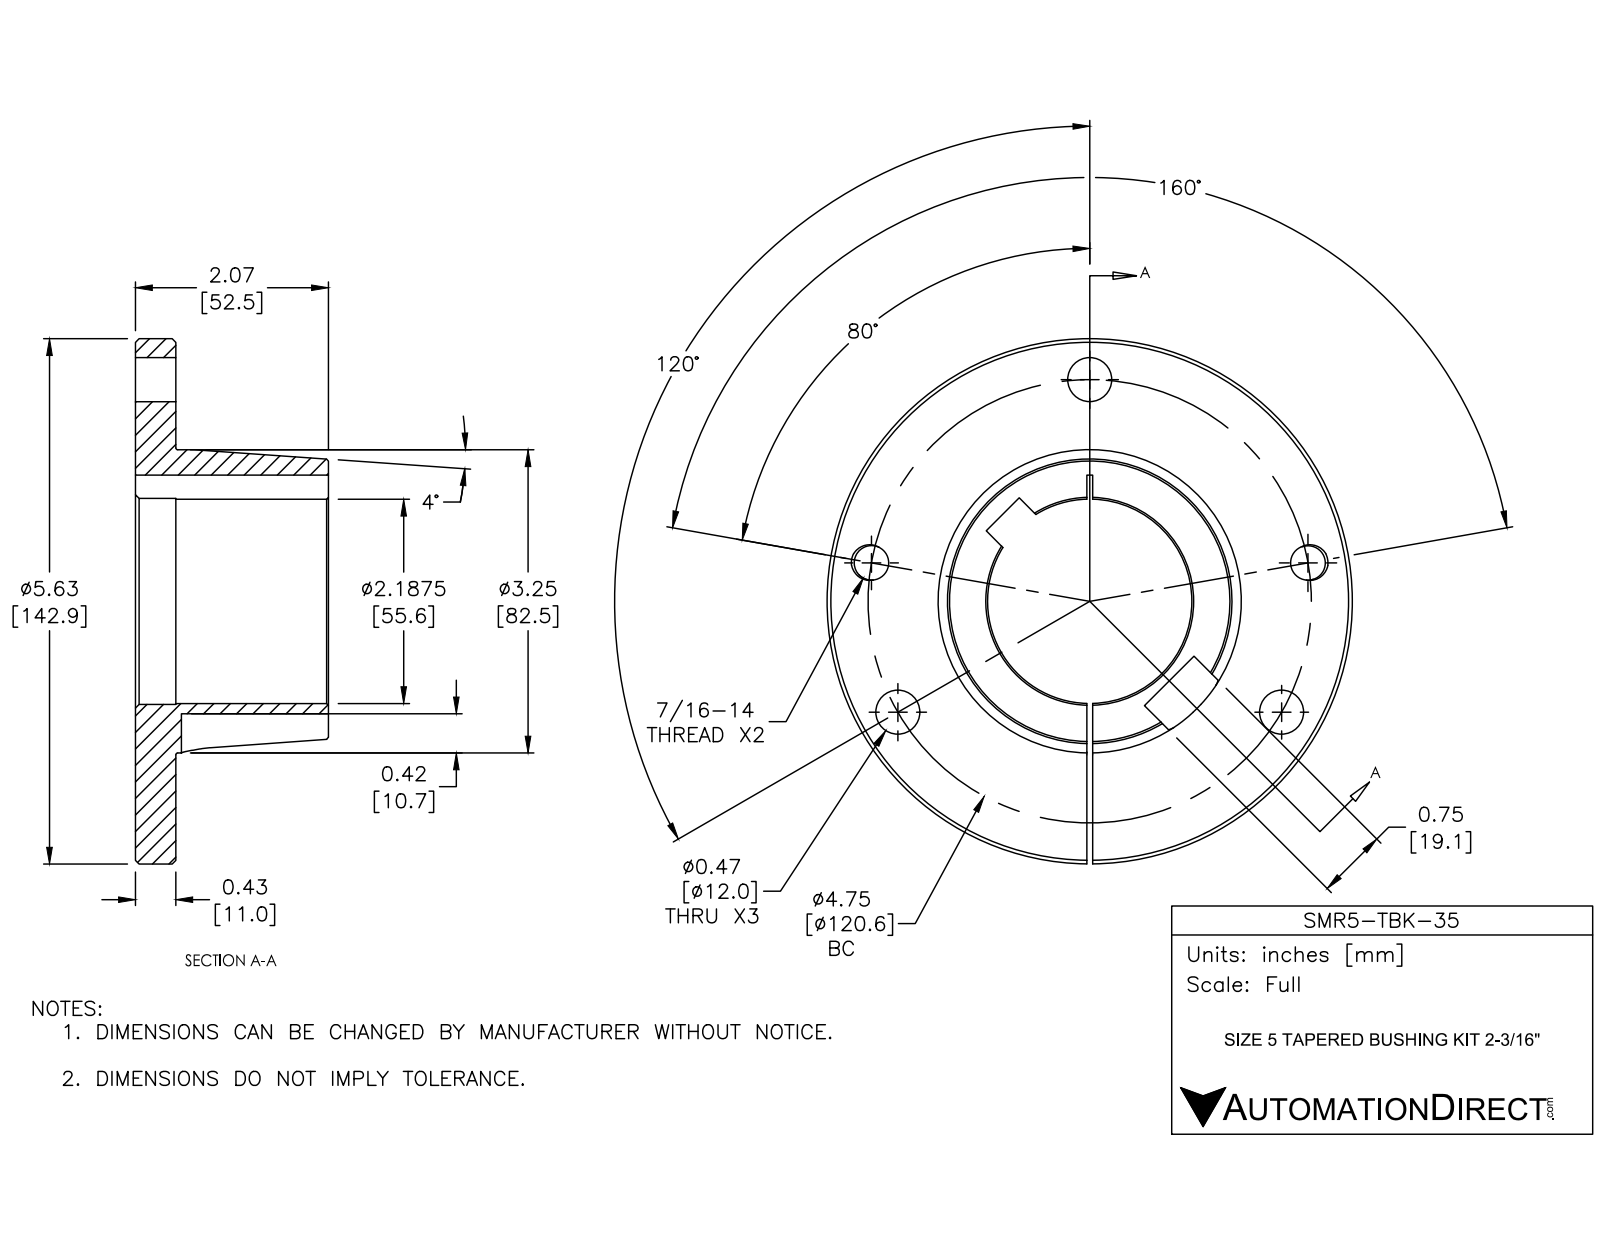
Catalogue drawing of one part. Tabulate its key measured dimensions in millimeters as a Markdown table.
| quantity | value |
| --- | --- |
| part name | SMR5-TBK-35 |
| STEP written by | SolidWorks 2016 (AUTOMOTIVE_DESIGN) |
| units | millimeters |
| bodies | 1 solid, 111 faces (18 planar, 71 cylindrical, 22 other) |
| overall size | 142.9 × 142.9 × 52.5 |
| volume | 239 700 mm³ |
| surface area | 55 180 mm² |
| round holes (diameter × count) | 12 × 3, 9.4 × 2, 10.9 × 2, 55.5 × 1, 56.1 × 1 |
| round bosses / shafts (diameter × count) | 142.9 × 1, 82.5 × 1 |
| partial cylindrical surfaces (radius × count) | 8 × 2 |
| main face-to-face distances | 11, 52.5, 41.5, 1.6, 64.1, 3.2, 15.9, 12.7, 19.1, 12.5 |
| hole center spacings | 60.3, 104.4, 118.8, 41.2, 77.5 |
